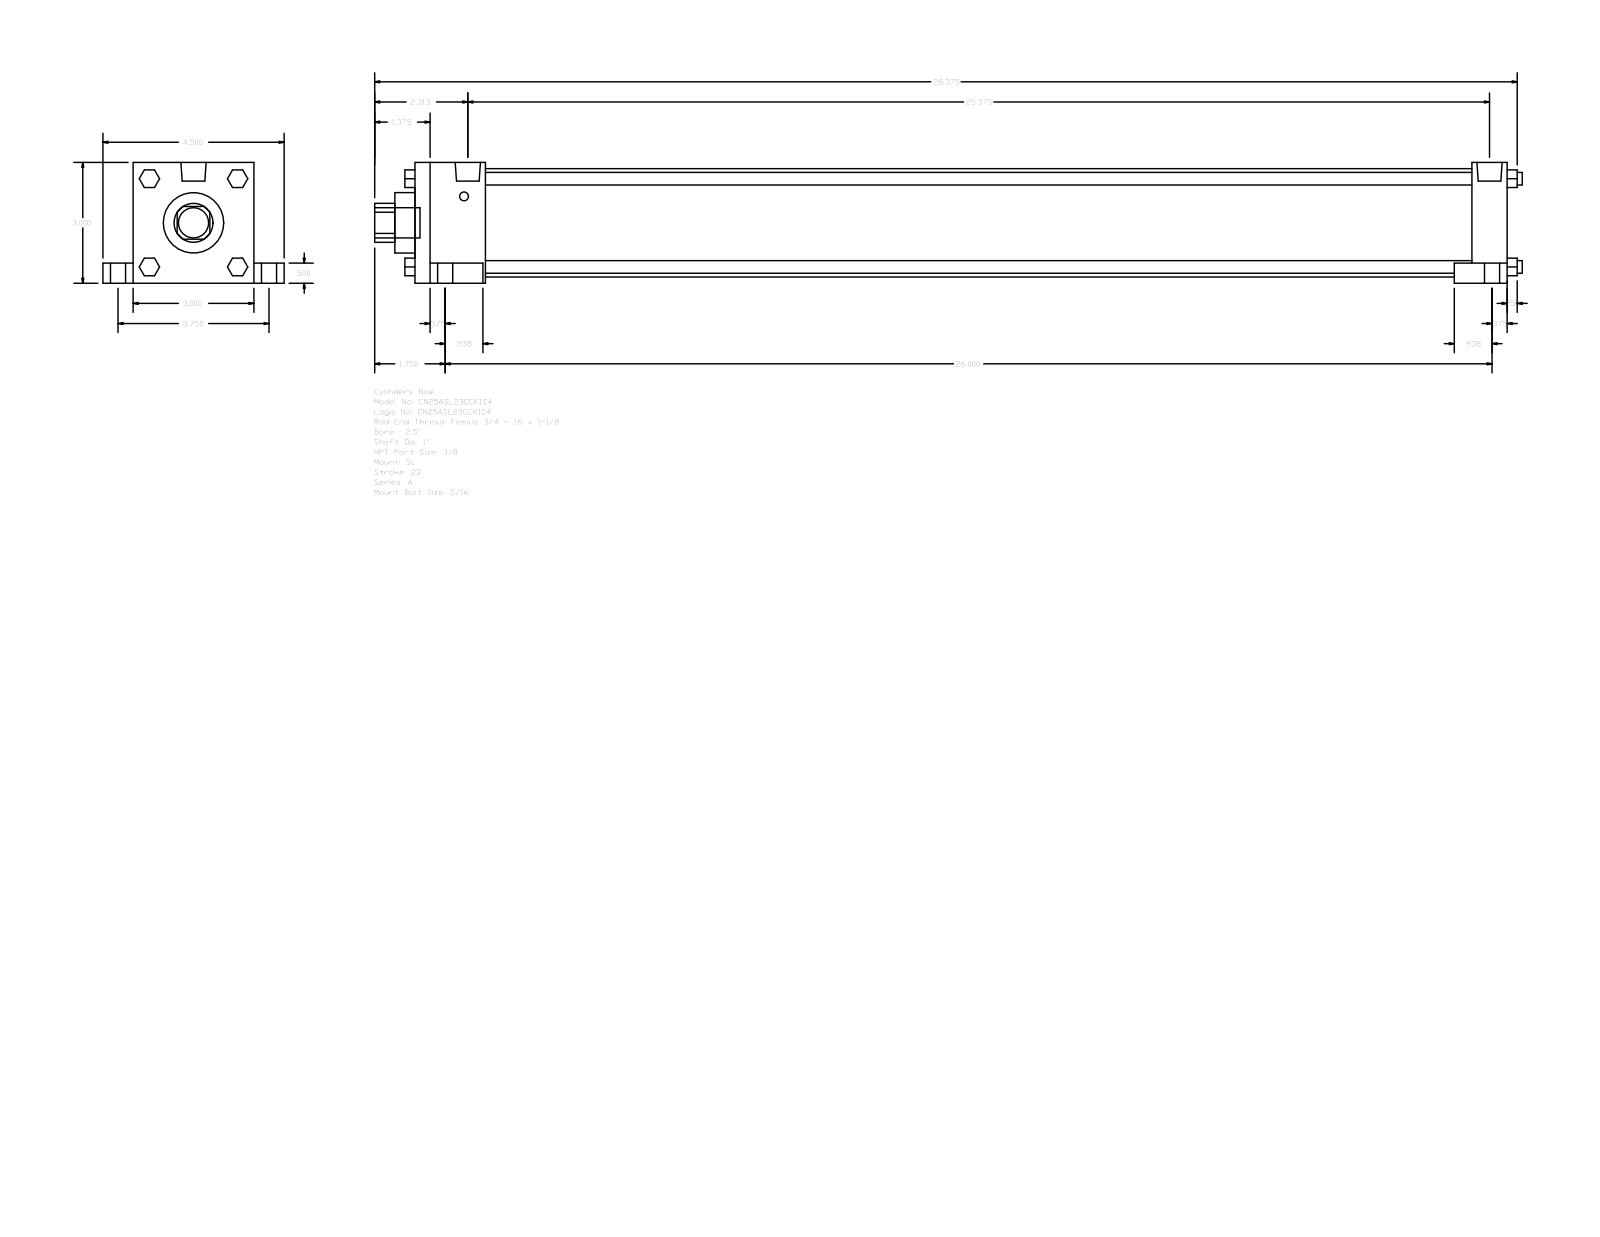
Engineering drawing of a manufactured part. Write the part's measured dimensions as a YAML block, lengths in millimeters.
part_name: "A_SL__0250_1"
step_written_by: "GSSL Pune (CONFIG_CONTROL_DESIGN)"
units: millimeters
bodies: {solids: 0, faces: 148, planar: 112, cylindrical: 36, other: 0}
overall_size: [723.9, 114.3, 76.2]
round_holes:
  - {diameter: 25.4, count: 1}
  - {diameter: 38.1, count: 1}
  - {diameter: 68.33, count: 1}
round_bosses_or_shafts:
  - {diameter: 15.88, count: 4}
  - {diameter: 9.53, count: 4}
  - {diameter: 7.94, count: 4}
  - {diameter: 5.56, count: 4}
  - {diameter: 15.93, count: 2}
  - {diameter: 19.05, count: 1}
partial_cylinders:
  - {radius: 12.29, count: 1}
face_to_face_distances: [76.2, 688.98, 12.7, 44.45, 644.53, 666.75, 622.3, 22.23, 19.05, 63.5]
